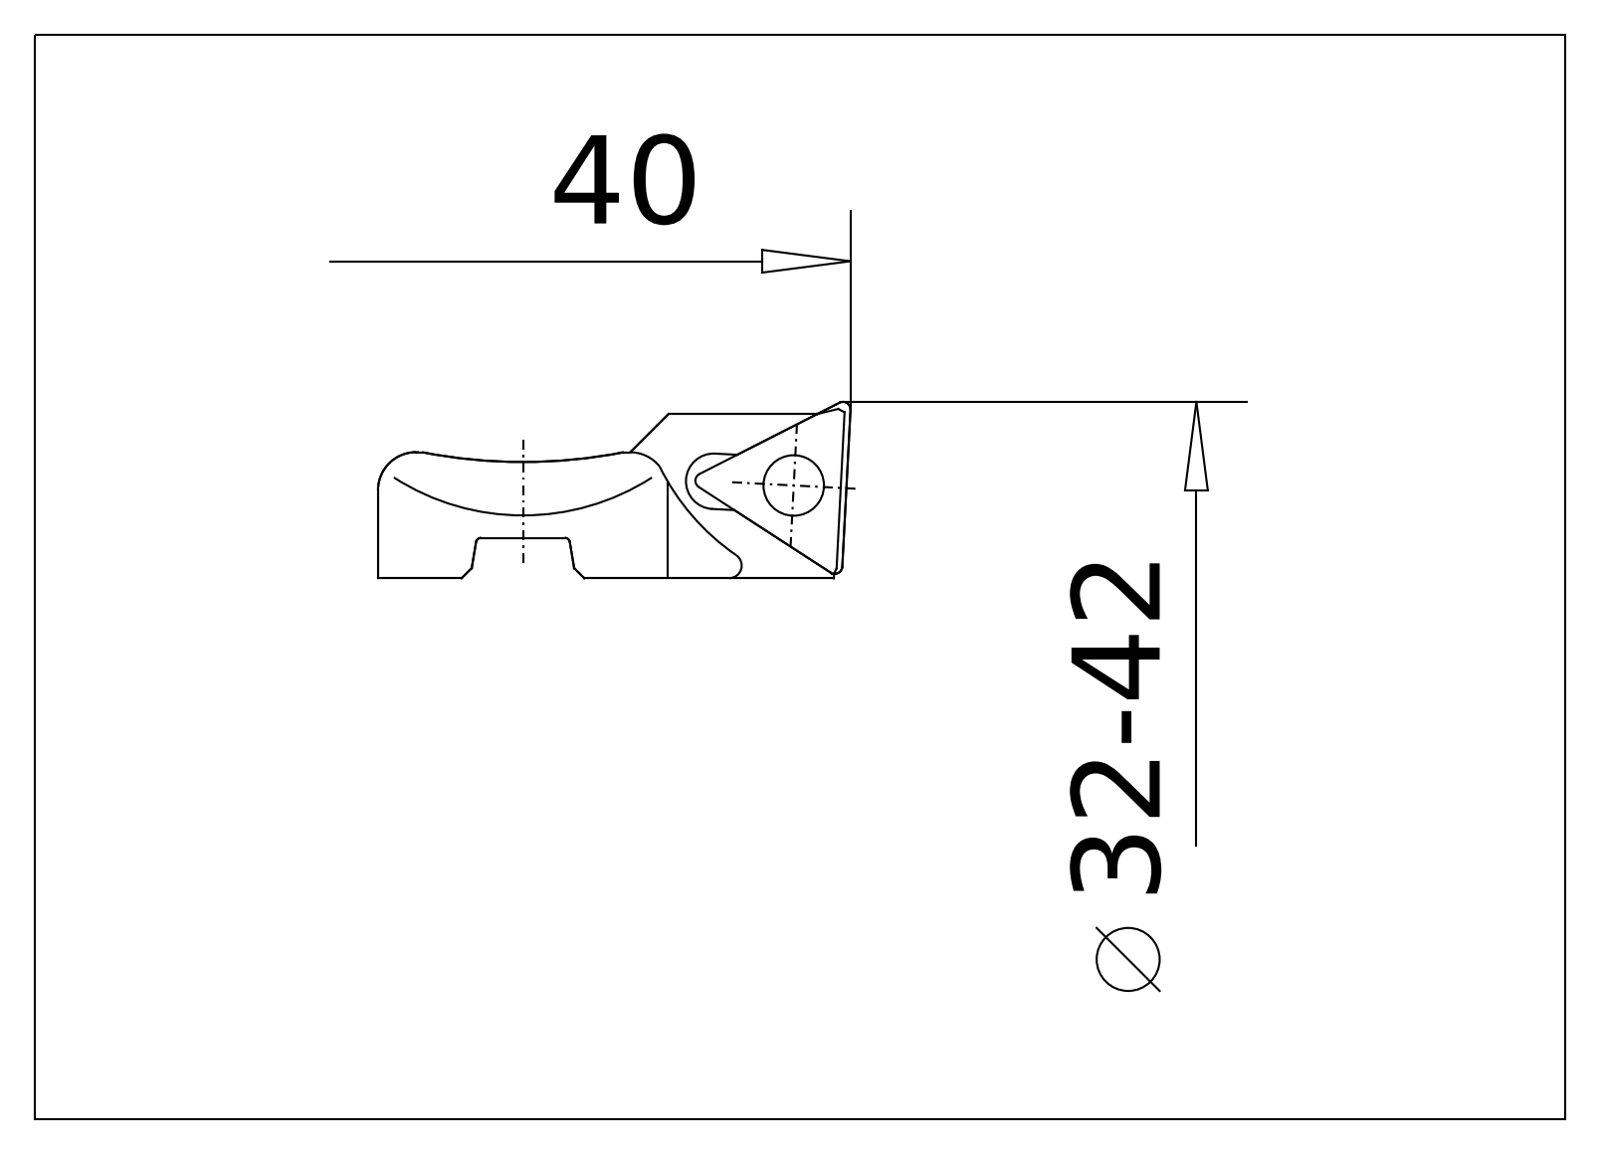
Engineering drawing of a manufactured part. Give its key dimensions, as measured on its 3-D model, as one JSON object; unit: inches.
{"part_name": "626.231 Kaiser EBH 31 TP07 32-42|694.103 Kaiser ETL M2x4.8 T6 IP 10S;Kreismuster1; 626.231 Kaiser EBH 31 TP07 32-42|651.735 Kaiser TPGT 070203 K10C;Kombinieren1; 626.231 Kaiser EBH 31 TP07 32-42|626.231 Kaiser EBH 31 TP07 32-42;Schnitt-Linear austragen4", "step_written_by": "ACIS (automotive_design)", "units": "inches", "bodies": {"solids": 3, "faces": 94, "planar": 29, "cylindrical": 37, "other": 28}, "overall_size": [0.733, 0.443, 0.276], "volume_in3": 0.033, "surface_area_in2": 1.22, "round_holes": [[0.061, 1], [0.091, 1], [0.159, 1], [0.307, 1]], "round_bosses_or_shafts": [[0.106, 1], [0.079, 1]], "partial_cylinders_radius": [[0.006, 6], [0.012, 6], [0.043, 1], [0.221, 1], [0.394, 1], [0.545, 1], [0.613, 1]], "face_to_face_distances": [0.065, 0.03, 0.094, 0.221, 0.098, 0.167, 0.039, 0.261, 0.013, 0.111]}
